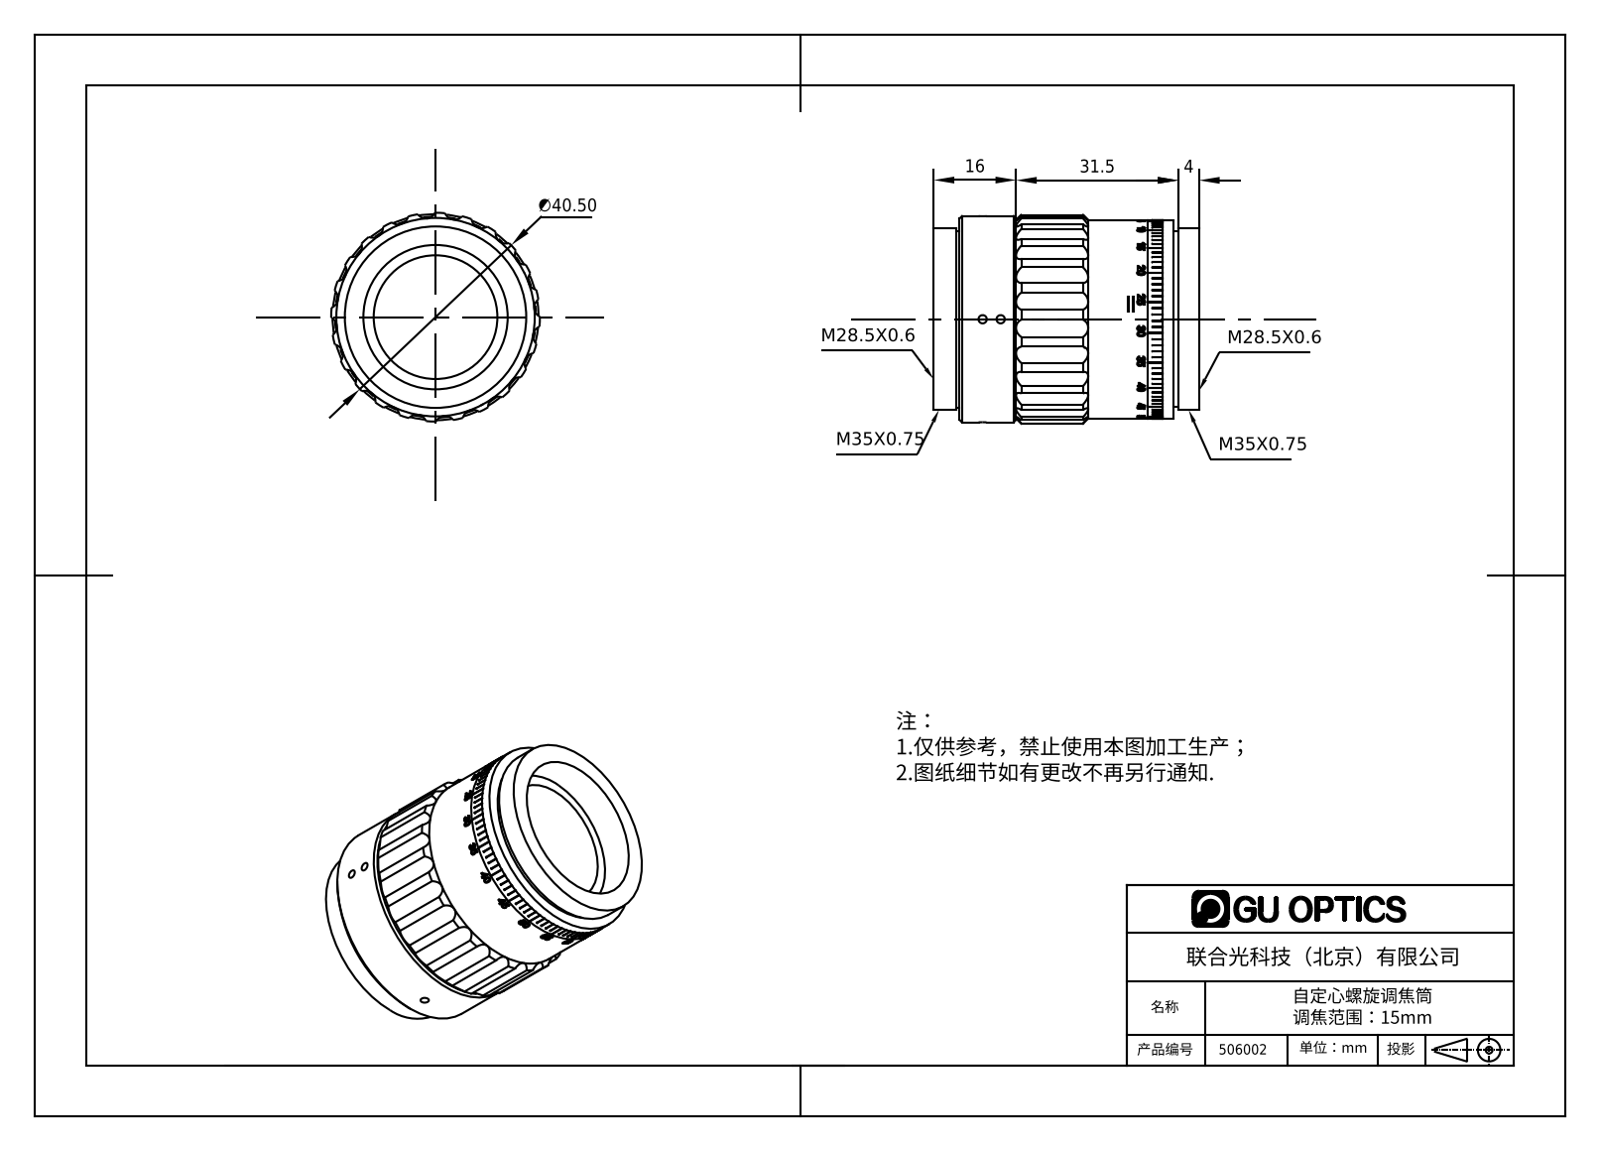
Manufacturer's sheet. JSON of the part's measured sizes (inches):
{"part_name": "HFA24-03调焦手轮; 506002; HFA24-02定位筒; 限位铜钉 (+2 more)", "step_written_by": "SolidWorks 2016 (AUTOMOTIVE_DESIGN)", "units": "inches", "bodies": {"solids": 8, "faces": 1559, "planar": 658, "cylindrical": 351, "other": 550}, "overall_size": [2.028, 1.594, 1.594], "volume_in3": 2.037, "surface_area_in2": 46.06, "round_holes": [[0.063, 5], [0.083, 2], [0.945, 1], [1.102, 1], [1.181, 1], [1.201, 1], [1.209, 1], [1.327, 1], [1.417, 1], [1.445, 1], [1.457, 1]], "round_bosses_or_shafts": [[0.081, 4], [0.079, 4], [1.575, 1], [1.516, 1], [1.441, 1], [1.398, 1], [1.386, 1], [1.378, 1]], "partial_cylinders_radius": [[0.079, 24], [0.6, 4], [0.591, 2], [0.685, 1], [0.757, 1], [0.797, 1]], "face_to_face_distances": [0.197, 0.472, 0.079, 0.039, 0.02, 1.831, 0.394, 1.358, 1.378, 1.634], "hole_center_spacings": [0.138]}
